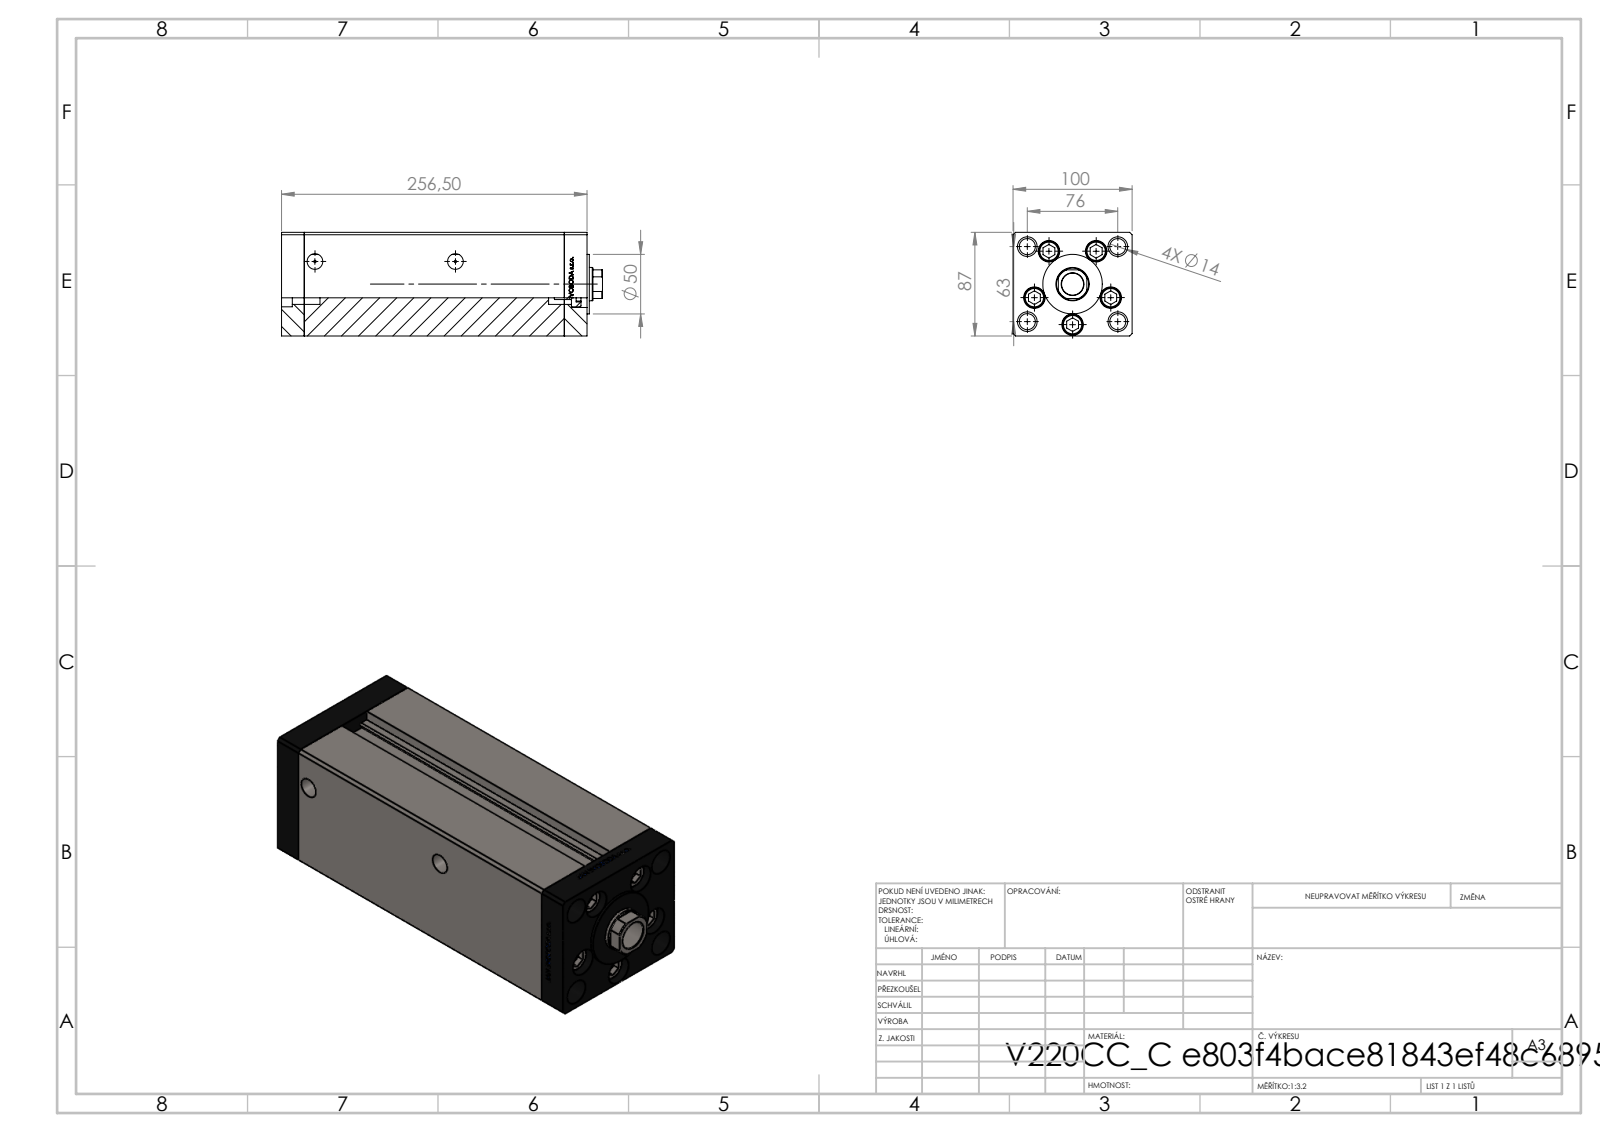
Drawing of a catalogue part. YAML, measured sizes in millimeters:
part_name: "V220C BACK_C; V220C FRONT; V220C_C MIDDLE; ALLEN BOLT (+1 more)"
step_written_by: "SolidWorks 2019 (CONFIG_CONTROL_DESIGN)"
units: millimeters
bodies: {solids: 13, faces: 1176, planar: 546, cylindrical: 168, other: 462}
overall_size: [269.5, 100, 87]
volume: 1824000
surface_area: 278174
round_holes:
  - {diameter: 13.5, count: 9}
  - {diameter: 18, count: 5}
  - {diameter: 12, count: 4}
  - {diameter: 16.5, count: 4}
  - {diameter: 2, count: 2}
  - {diameter: 13.16, count: 2}
  - {diameter: 17, count: 1}
  - {diameter: 18.5, count: 1}
  - {diameter: 28, count: 1}
round_bosses_or_shafts:
  - {diameter: 8, count: 5}
  - {diameter: 17, count: 4}
  - {diameter: 50, count: 1}
partial_cylinders:
  - {radius: 0.93, count: 2}
  - {radius: 13.5, count: 1}
face_to_face_distances: [100, 87, 19, 218.5, 237.5, 34.25, 256.5, 222.25, 203.25, 15.25]
hole_center_spacings: [34, 49.36, 18.59, 21.03, 38.08, 39.27, 40.83, 43.24]
